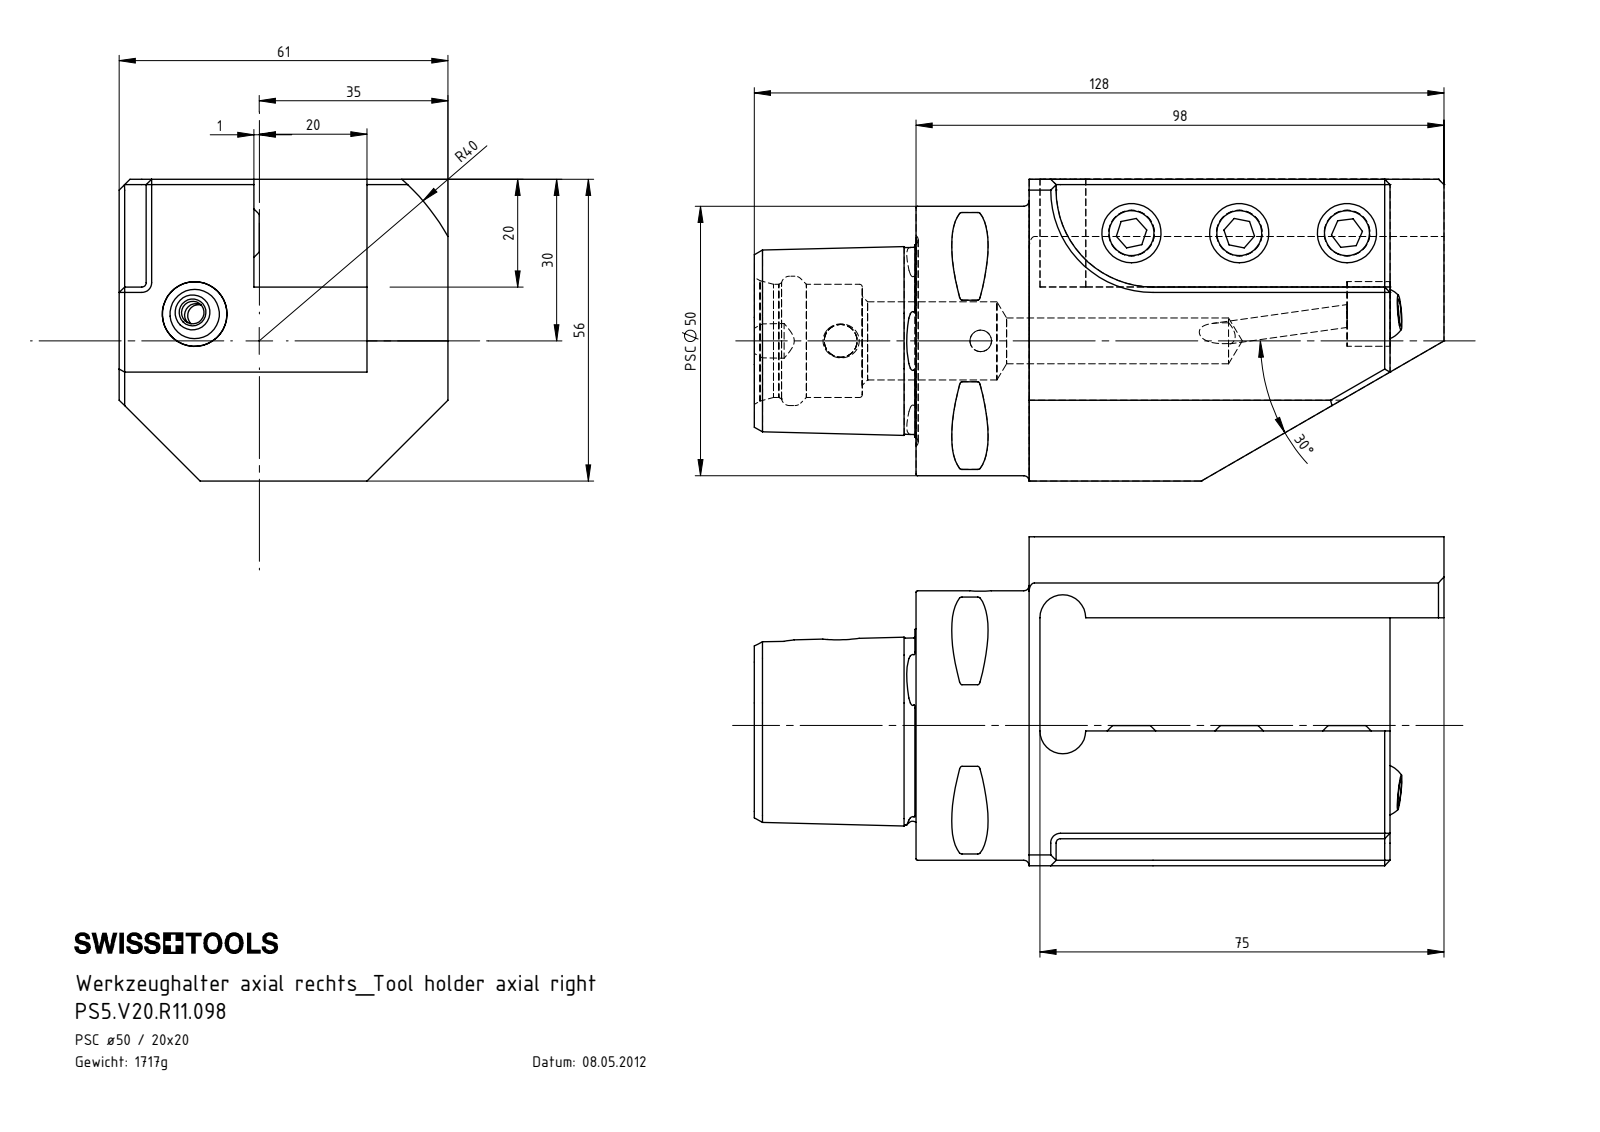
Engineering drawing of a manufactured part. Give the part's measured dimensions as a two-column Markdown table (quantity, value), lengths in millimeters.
| quantity | value |
| --- | --- |
| part name | KU1-U12.001.010_2; ISO 4026 - M10 x 20; PS5-V20.R11.098_A; KU1-U12.001.010 (+2 more) |
| STEP written by | SolidWorks 2012 (CONFIG_CONTROL_DESIGN) |
| units | millimeters |
| bodies | 6 solids, 241 faces (79 planar, 56 cylindrical, 106 other) |
| overall size | 128 × 61 × 56 |
| volume | 218 987 mm³ |
| surface area | 38 445 mm² |
| round holes (diameter × count) | 8.5 × 4, 4.2 × 2, 4 × 1, 6.1 × 1, 7 × 1, 12 × 1, 14.5 × 1, 21 × 1, 24 × 1 |
| round bosses / shafts (diameter × count) | 10 × 3, 50 × 1 |
| partial cylindrical surfaces (radius × count) | 0.5 × 8, 0.8 × 2, 4.25 × 2, 4 × 1, 18 × 1, 40 × 1 |
| main face-to-face distances | 20, 36, 21, 56, 15, 61, 46, 67, 25, 5 |
| hole center spacings | 20, 13, 26, 34.41, 40, 52, 57.58, 70.88 |
